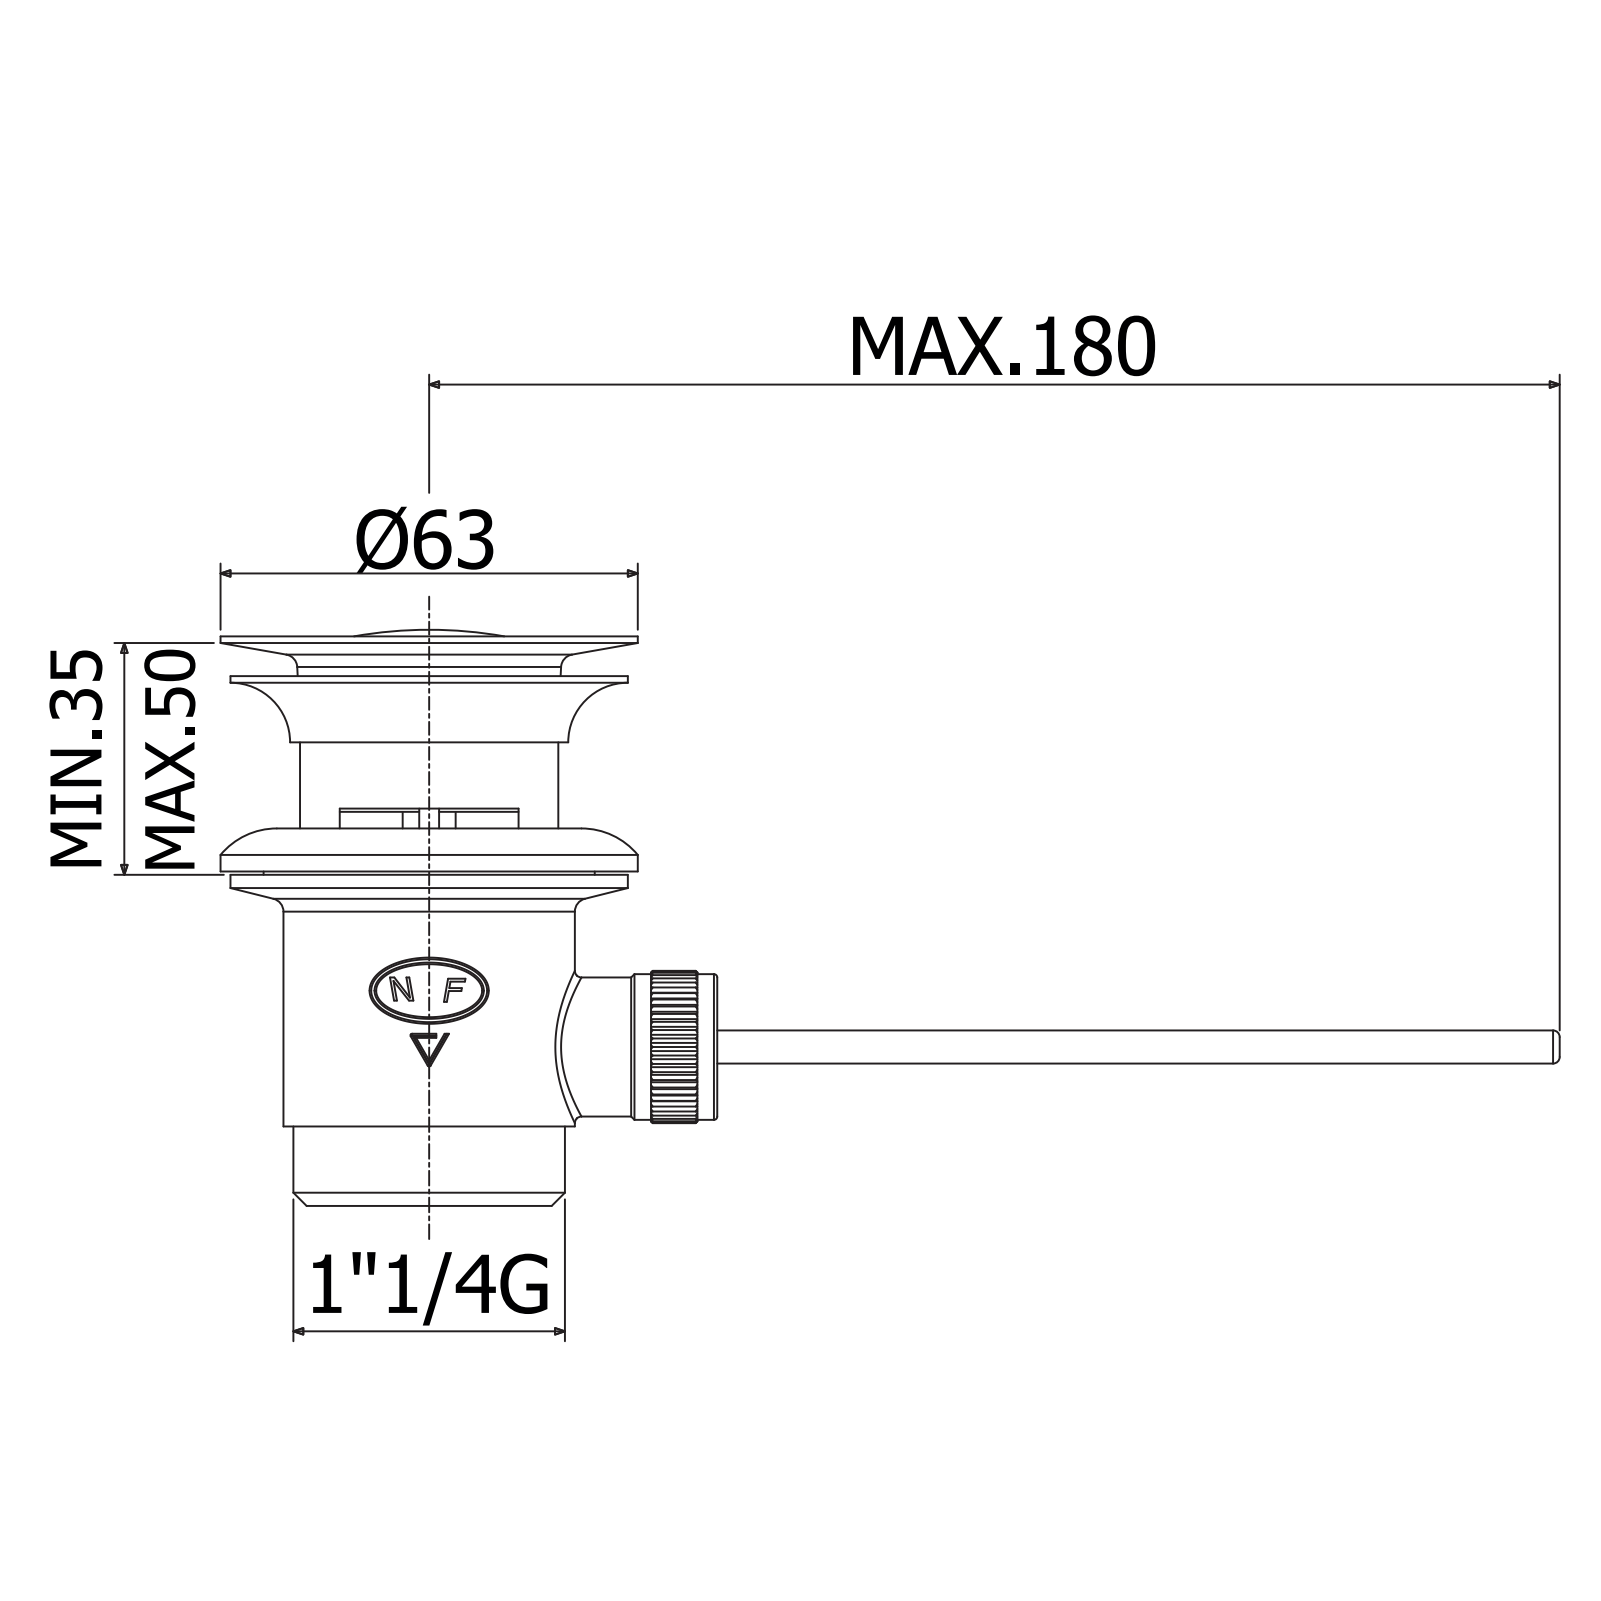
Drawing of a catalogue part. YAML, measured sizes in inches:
part_name: "ZSCA002CR"
step_written_by: "CREO PARAMETRIC BY PTC INC, 2020044 (CONFIG_CONTROL_DESIGN)"
units: inches
bodies: {solids: 2, faces: 648, planar: 347, cylindrical: 96, other: 205}
overall_size: [8.391, 3.425, 2.48]
volume: 3.94
surface_area: 83.48
round_holes:
  - {diameter: 0.413, count: 1}
  - {diameter: 0.472, count: 1}
  - {diameter: 0.531, count: 1}
  - {diameter: 0.551, count: 1}
  - {diameter: 0.61, count: 1}
  - {diameter: 0.744, count: 1}
  - {diameter: 1.161, count: 1}
  - {diameter: 1.319, count: 1}
  - {diameter: 1.417, count: 1}
  - {diameter: 1.531, count: 1}
  - {diameter: 1.634, count: 1}
  - {diameter: 2.205, count: 1}
round_bosses_or_shafts:
  - {diameter: 2.48, count: 1}
  - {diameter: 2.362, count: 1}
  - {diameter: 1.969, count: 1}
  - {diameter: 1.732, count: 1}
  - {diameter: 1.614, count: 1}
  - {diameter: 1.535, count: 1}
  - {diameter: 1.437, count: 1}
  - {diameter: 1.378, count: 1}
partial_cylinders:
  - {radius: 0.01, count: 8}
  - {radius: 0.118, count: 2}
  - {radius: 0.197, count: 1}
  - {radius: 0.217, count: 1}
  - {radius: 0.825, count: 1}
face_to_face_distances: [0.118, 0.059, 1.28, 0.039, 0.315, 1.221, 0.591, 1.772, 0.256, 0.394]
